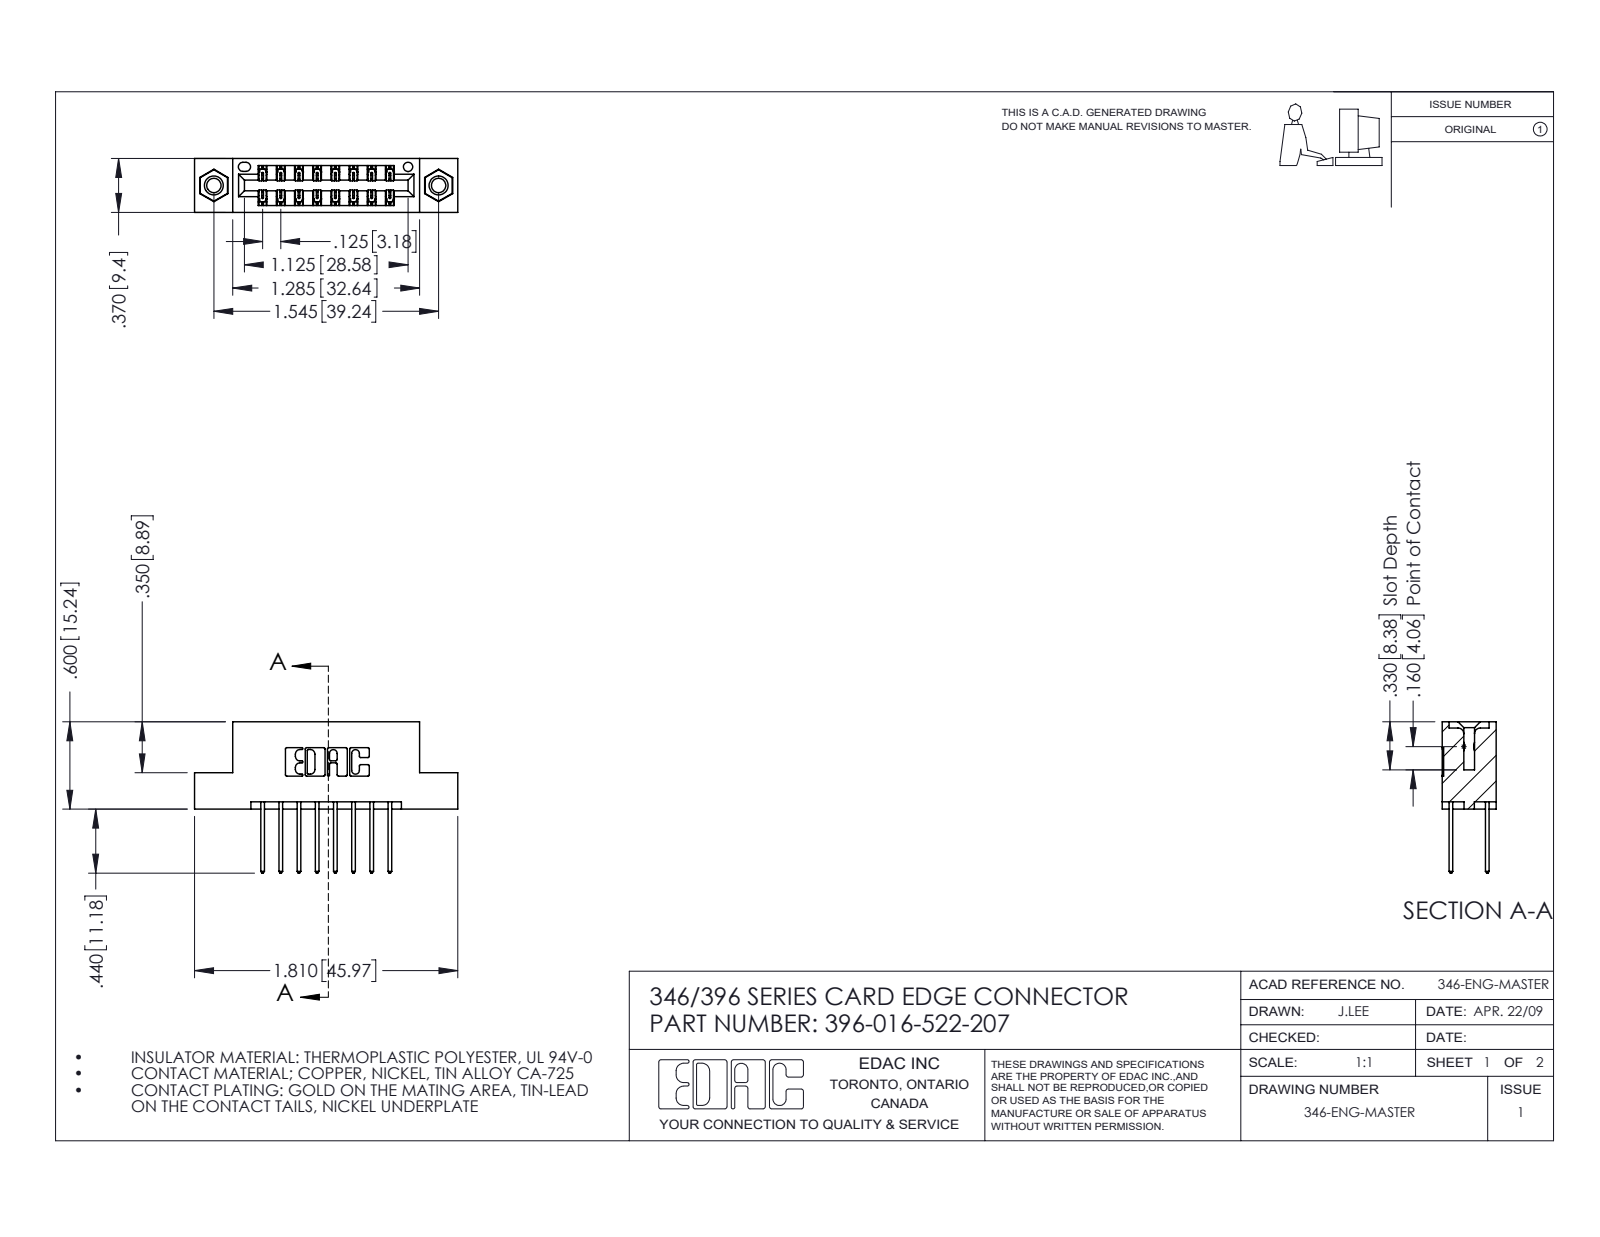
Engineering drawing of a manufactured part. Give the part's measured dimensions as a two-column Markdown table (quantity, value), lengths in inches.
| quantity | value |
| --- | --- |
| part name | 346 Part_Flush Mounting Lugs - 0.156 Dia-TI; 345-292-001_345-293-122; 396-016-522-207; 345-250-001_345-250-005-103 |
| STEP written by | SolidWorks 2016 (CONFIG_CONTROL_DESIGN) |
| units | inches |
| bodies | 19 solids, 1014 faces (668 planar, 330 cylindrical, 16 other) |
| overall size | 1.81 × 1.04 × 0.37 |
| volume | 0.259 in³ |
| surface area | 8.566 in² |
| round holes (diameter × count) | 0.098 × 2, 0.125 × 2, 0.156 × 2, 0.064 × 1 |
| round bosses / shafts (diameter × count) | 0.155 × 2 |
| partial cylindrical surfaces (radius × count) | 0.006 × 24, 0.01 × 22, 0.01 × 16, 0.007 × 6, 0.031 × 6, 0.026 × 3, 0.014 × 2, 0.022 × 2 |
| main face-to-face distances | 0.25, 0.048, 0.322, 0.37, 0.072, 0.298, 0.025, 0.275, 0.5, 0.148 |
| hole center spacings | 0.246, 1.341, 1.545 |
